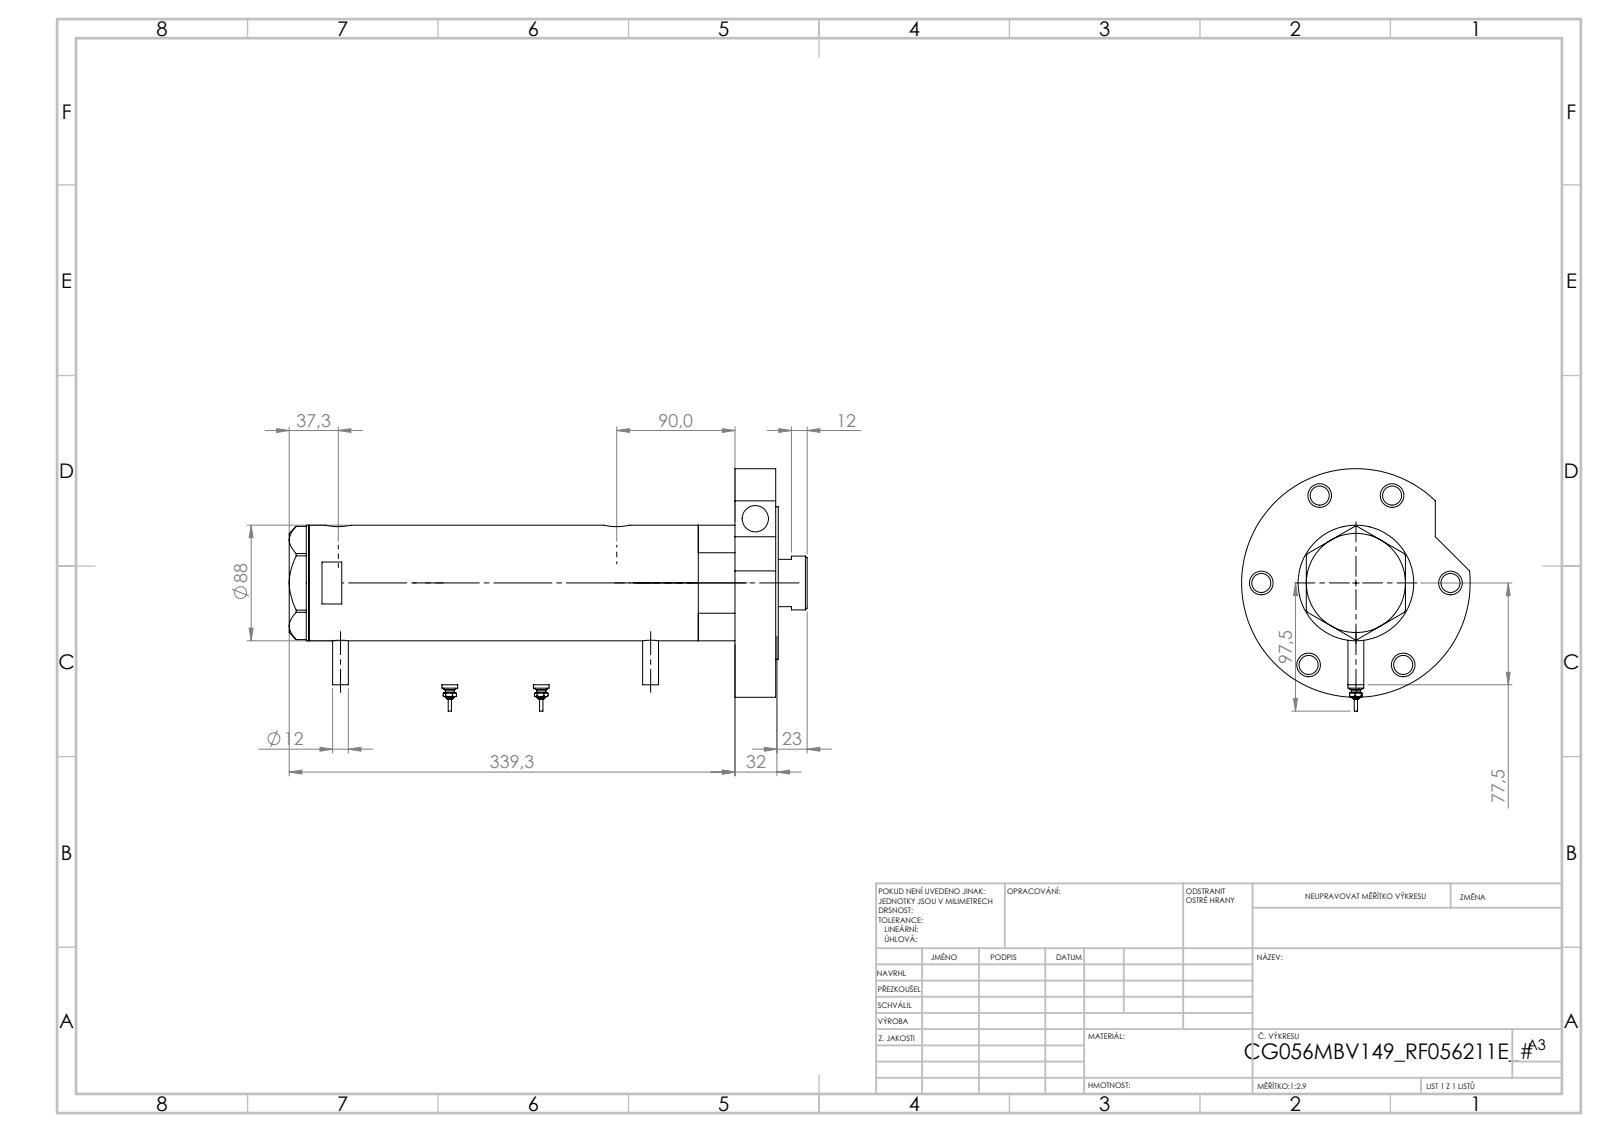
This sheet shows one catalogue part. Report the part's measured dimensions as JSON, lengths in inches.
{"part_name": "V270CG_MIDDLE; Switch; V270CG_FRONT; V270CG_BACK (+2 more)", "step_written_by": "SolidWorks 2019 (CONFIG_CONTROL_DESIGN)", "units": "inches", "bodies": {"solids": 7, "faces": 257, "planar": 91, "cylindrical": 102, "other": 64}, "overall_size": [15.524, 7.264, 6.85], "volume_in3": 156.3, "surface_area_in2": 559.1, "round_holes": [[0.571, 7], [0.709, 6], [0.787, 3], [0.492, 2], [0.518, 2], [1.654, 1], [1.713, 1], [2.205, 1], [2.362, 1], [2.953, 1], [3.15, 1]], "round_bosses_or_shafts": [[0.472, 4], [0.354, 2], [0.276, 2], [0.177, 2], [0.098, 2], [6.85, 1], [4.567, 1], [3.465, 1]], "face_to_face_distances": [1.22, 0.079, 14.067, 12.768, 13.988, 1.299, 9.228, 3.539, 4.76, 4.839], "hole_center_spacings": [2.835, 3.15, 4.714, 4.91, 5.085, 5.657, 0.067, 1.016]}
